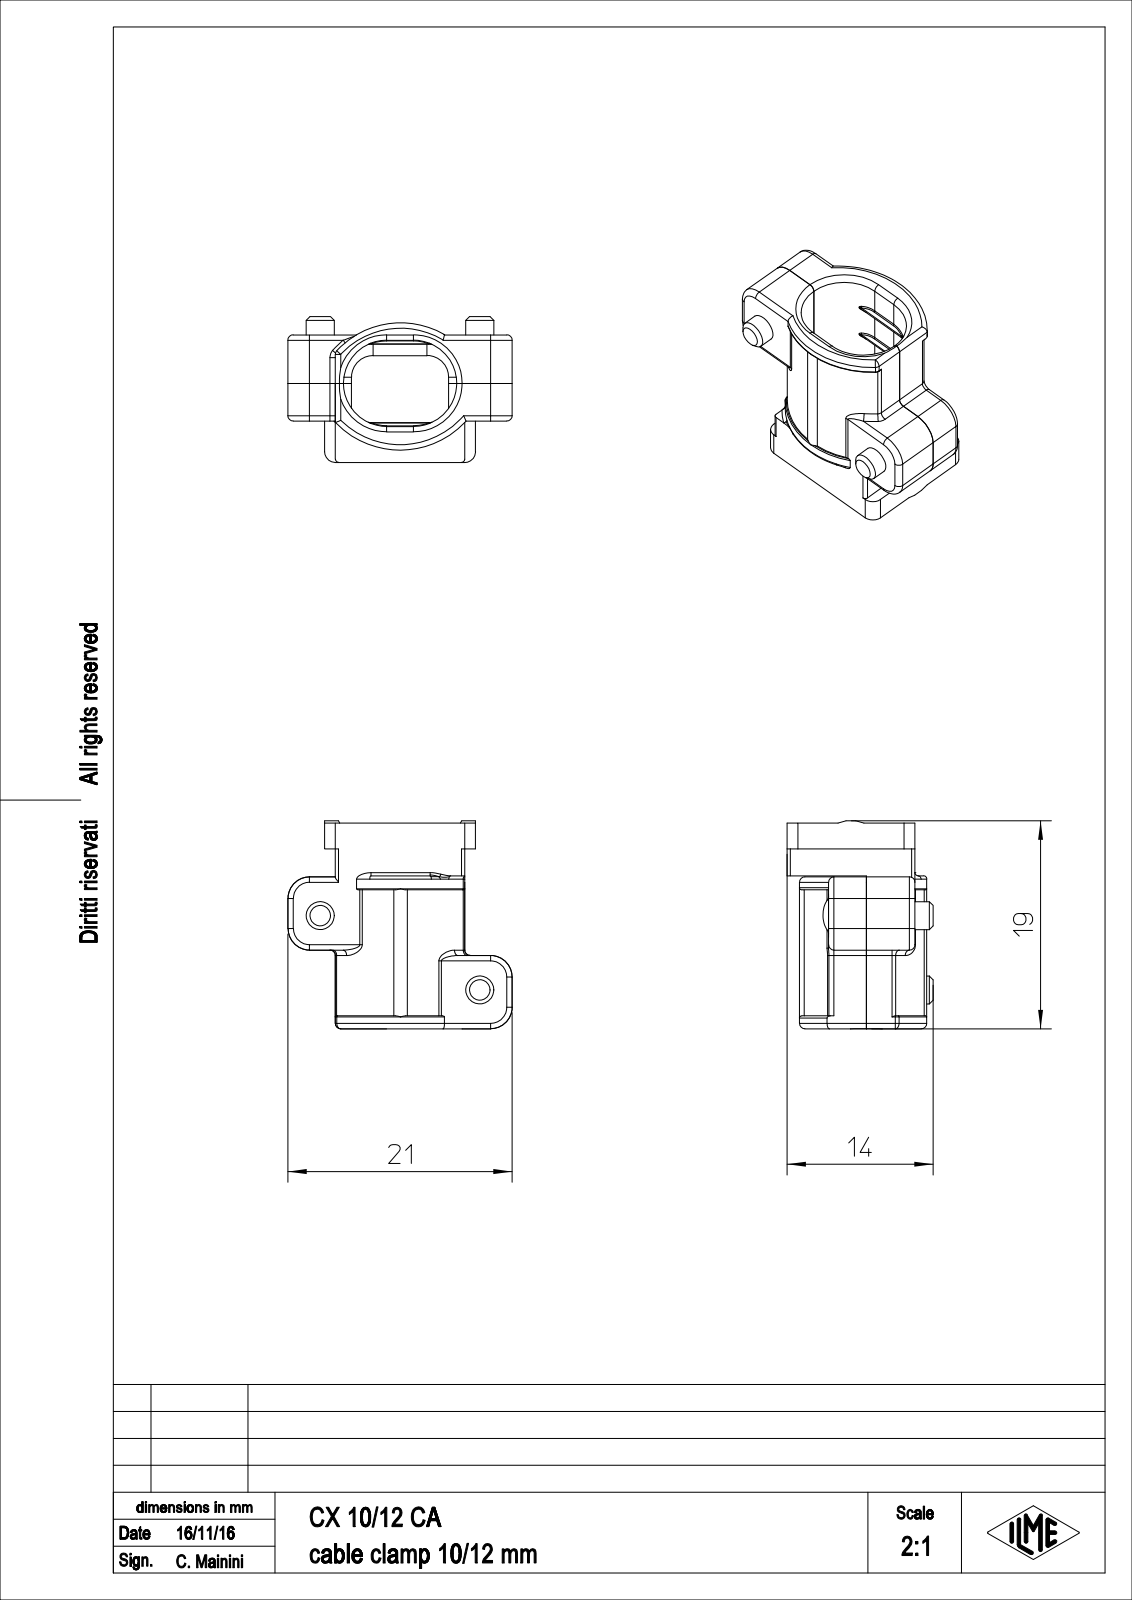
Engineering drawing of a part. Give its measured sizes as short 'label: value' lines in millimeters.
name: CX_10-12_CA
written by: PTC Creo Elements/Direct Modeling 19.0E 27-Jun-2016 (C) Parametric Technology GmbH (AUTOMOTIVE_DESIGN)
unit: mm
bodies: 1 solid, 398 faces (107 planar, 138 cylindrical, 153 other)
size: 20.8 × 19.3 × 13.55
volume: 1 548 mm³; area: 1 996 mm²
holes: 2× ⌀2.65
bosses: 2× ⌀2.6, 2× ⌀2.2
rounds: 44× R0.2, 35× R0.5, 8× R2, 6× R0.1, 6× R1, 5× R0.3, 2× R2.25, 2× R2.4
face distances: 8, 12, 0.5, 2.5, 11.85, 13, 1, 1.92, 1.42, 4.9
hole spacings: 16.37
